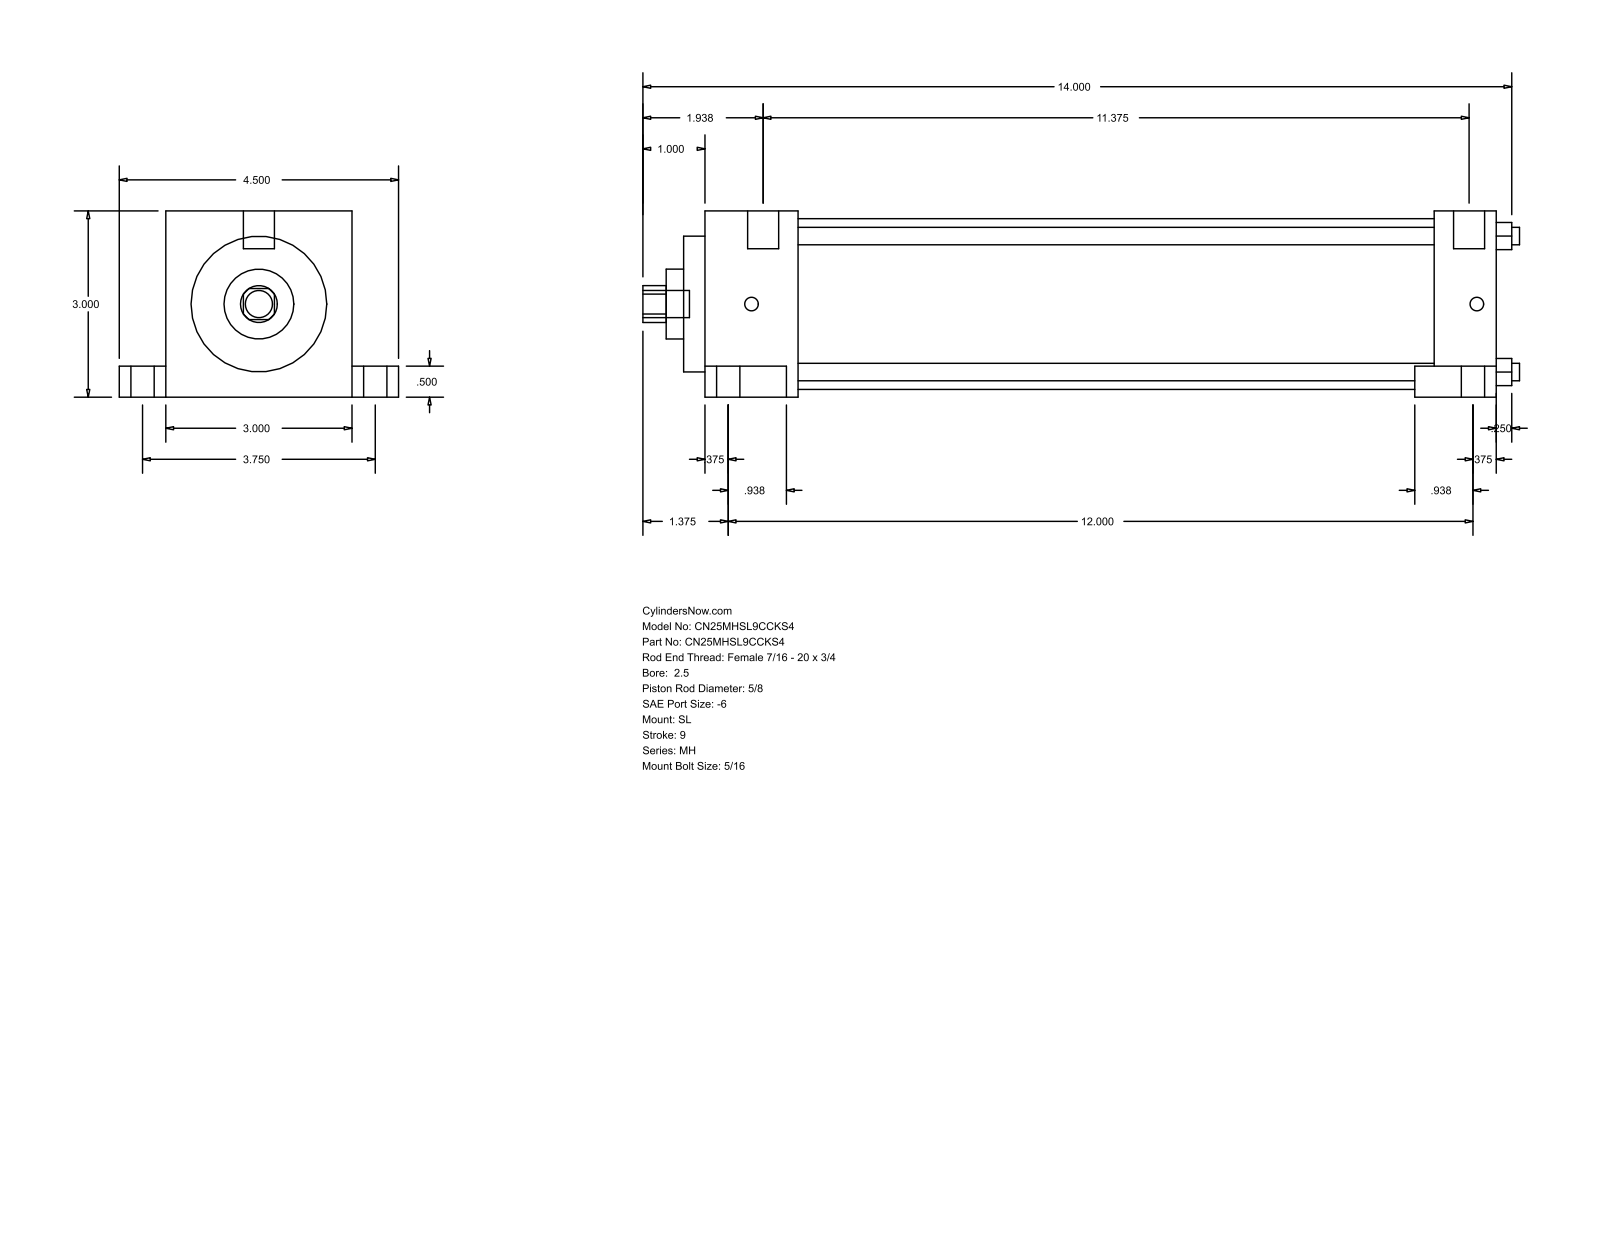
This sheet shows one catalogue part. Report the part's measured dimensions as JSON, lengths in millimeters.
{"part_name": "MH_SL__0250_0.625", "step_written_by": "GSSL Pune (CONFIG_CONTROL_DESIGN)", "units": "millimeters", "bodies": {"solids": 0, "faces": 86, "planar": 61, "cylindrical": 25, "other": 0}, "overall_size": [358.77, 114.3, 76.2], "round_holes": [[7.14, 4], [15.88, 1], [28.57, 1], [55.55, 1], [69.85, 1]], "round_bosses_or_shafts": [[15.88, 2], [9.53, 2], [5.56, 2], [12.7, 1], [11.11, 1]], "partial_cylinders_radius": [[7.54, 1]], "face_to_face_distances": [76.2, 25.4, 307.18, 332.58, 12.7, 63.5, 19.05, 95.25, 339.72, 31.75], "hole_center_spacings": [39.33, 55.62, 78.66]}
